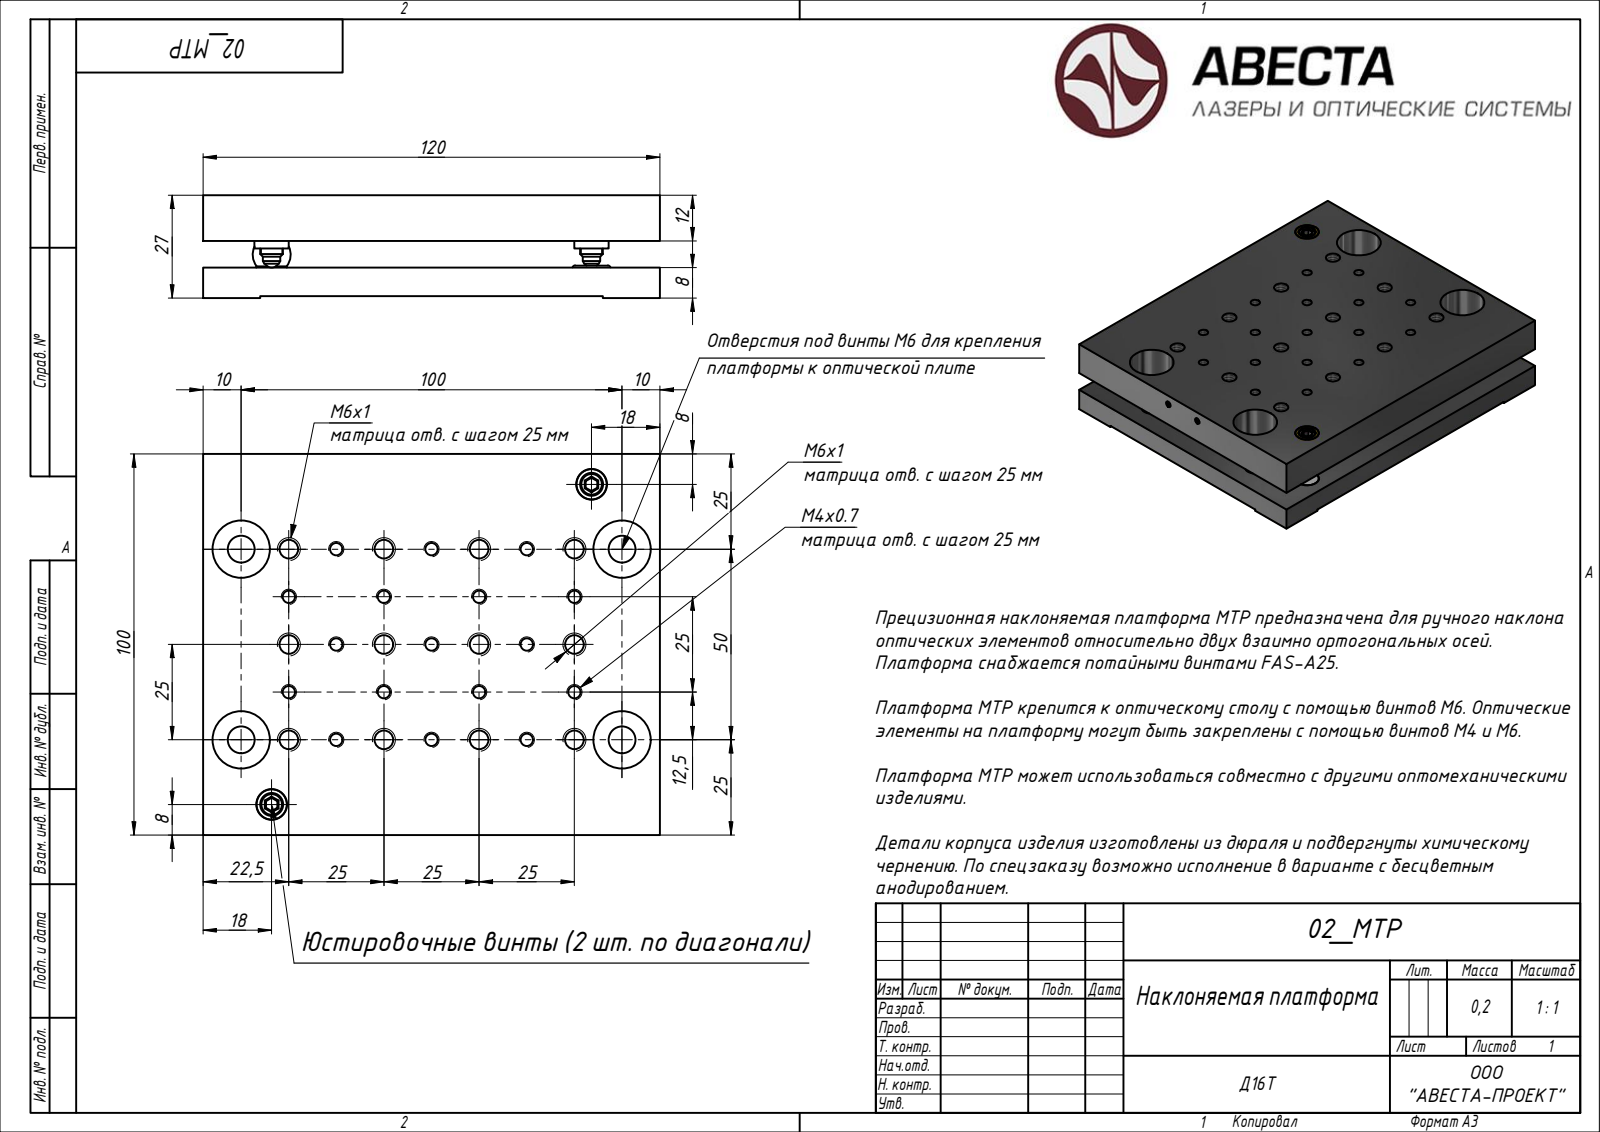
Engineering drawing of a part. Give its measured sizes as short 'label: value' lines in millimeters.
written by: Rhino 7.34 (AUTOMOTIVE_DESIGN)
unit: mm
bodies: 6 solids, 364 faces (122 planar, 176 cylindrical, 66 other)
size: 120 × 100 × 27
volume: 218 499 mm³; area: 66 609 mm²
holes: 17× ⌀3.24, 8× ⌀4.92, 6× ⌀6, 4× ⌀2.2, 4× ⌀7, 4× ⌀15, 2× ⌀8.05, 1× ⌀4, 1× ⌀4.92, 1× ⌀8.1, 1× ⌀10.1, 1× ⌀12.1
bosses: 7× ⌀2, 3× ⌀8, 2× ⌀9, 2× ⌀4.6, 1× ⌀2.5
rounds: 6× R1.1, 5× R1.25, 3× R2.46, 3× R2.46
face distances: 19, 7.5, 26.5, 7, 12, 14.5, 100, 120, 15, 8
hole spacings: 27.95, 25, 39.53, 12.5, 17.68, 35.36, 45.07, 51.54
